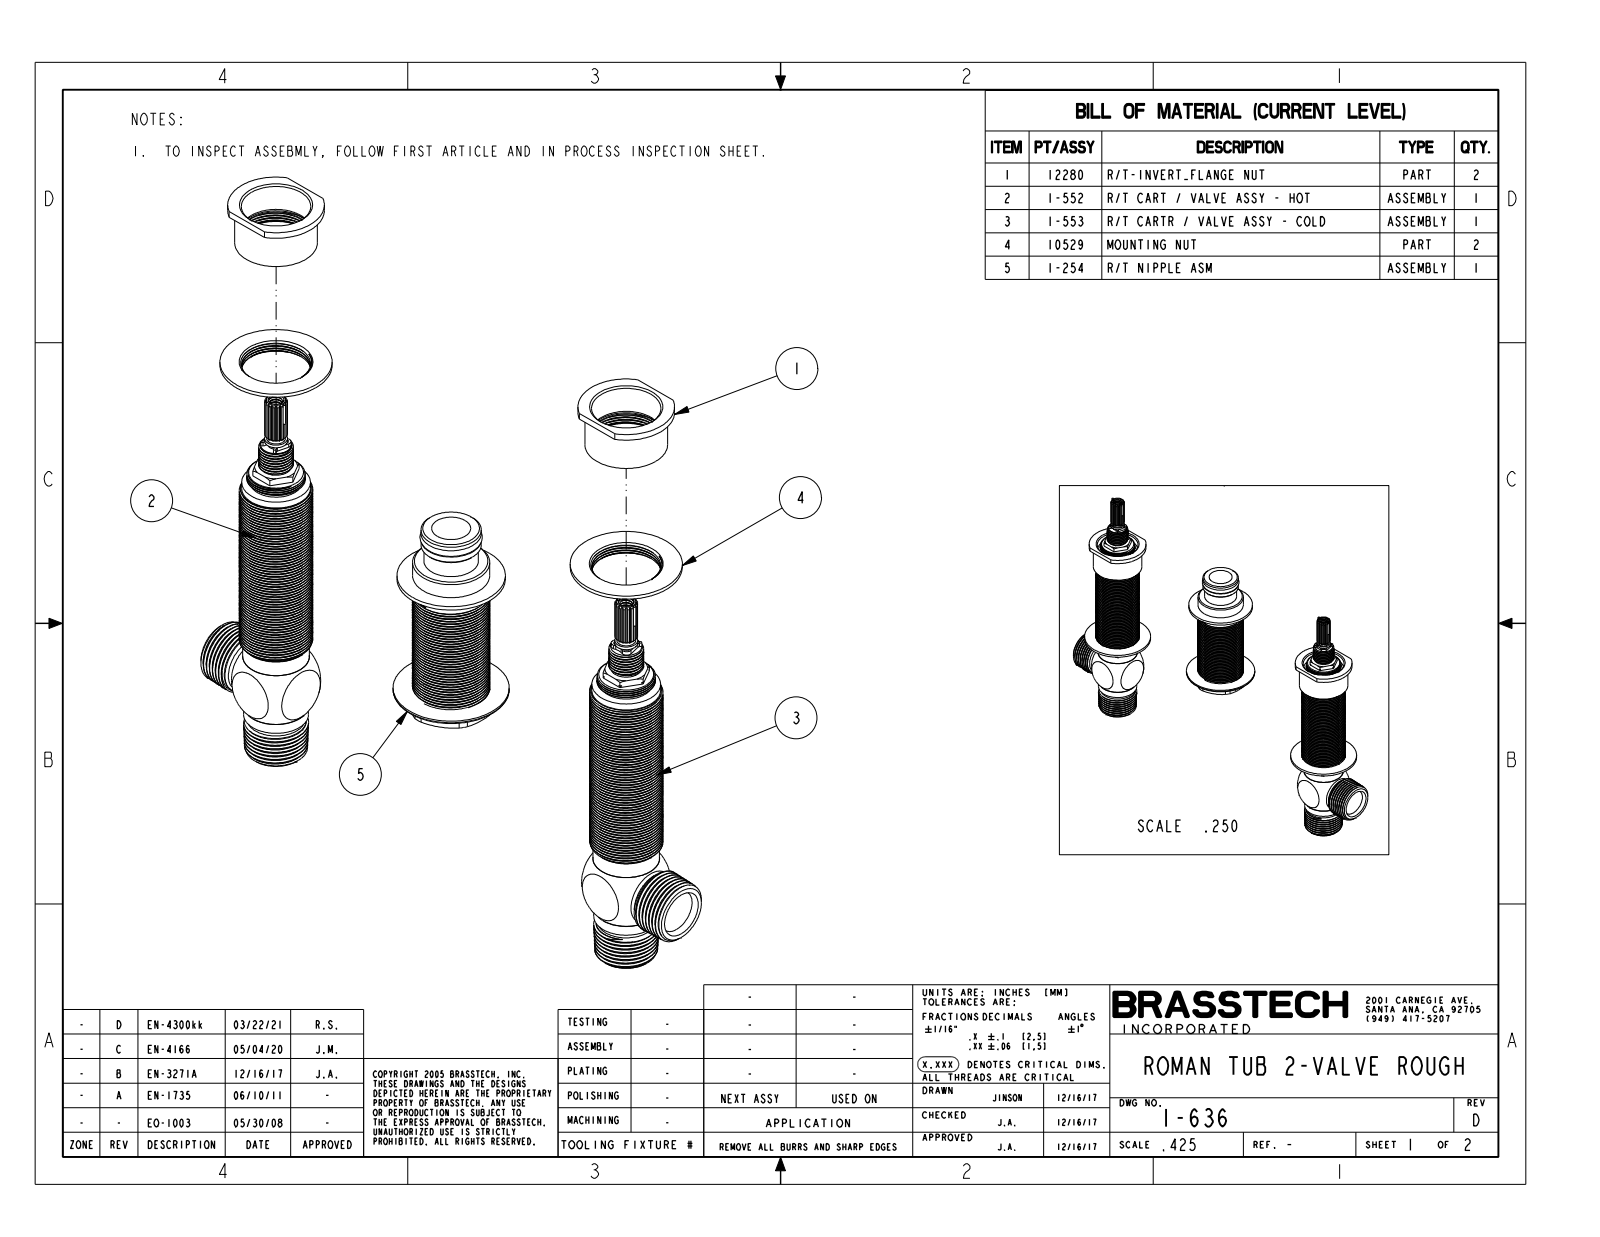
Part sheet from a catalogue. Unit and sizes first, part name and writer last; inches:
Units: inches
Overall size (bounding box): 10.52 × 6.941 × 1.875
Round holes (diameter × count): ⌀0.196 ×2, ⌀0.201 ×2, ⌀1.12 ×2, ⌀0.709 ×1, ⌀1.18 ×1
Round bosses / shafts (diameter × count): ⌀1.811 ×2, ⌀1.335 ×2, ⌀1.187 ×2, ⌀1.11 ×2, ⌀1.075 ×2, ⌀1.047 ×2, ⌀0.945 ×2, ⌀0.929 ×2
Partial cylindrical surfaces — rounded edges, fillets, slot ends (radius × count): R0.04 ×8, R0.08 ×8, R0.164 ×2, R0.26 ×2, R0.3 ×2, R0.775 ×2, R0.78 ×2, R0.758 ×1
Main face-to-face distances: 0.061, 3.061, 3, 3.171, 3.11, 0.11, 0.905, 0.844, 2.156, 2.266
Hole centre spacings: 8
Volume: 17.15 in³ · Surface area: 120.6 in²
Bodies: 3 solids, 1178 faces (230 planar, 526 cylindrical, 422 other)
Part name (STEP PRODUCT): 1-636
STEP written by: CREO PARAMETRIC BY PTC INC, 2018400 (AUTOMOTIVE_DESIGN)
